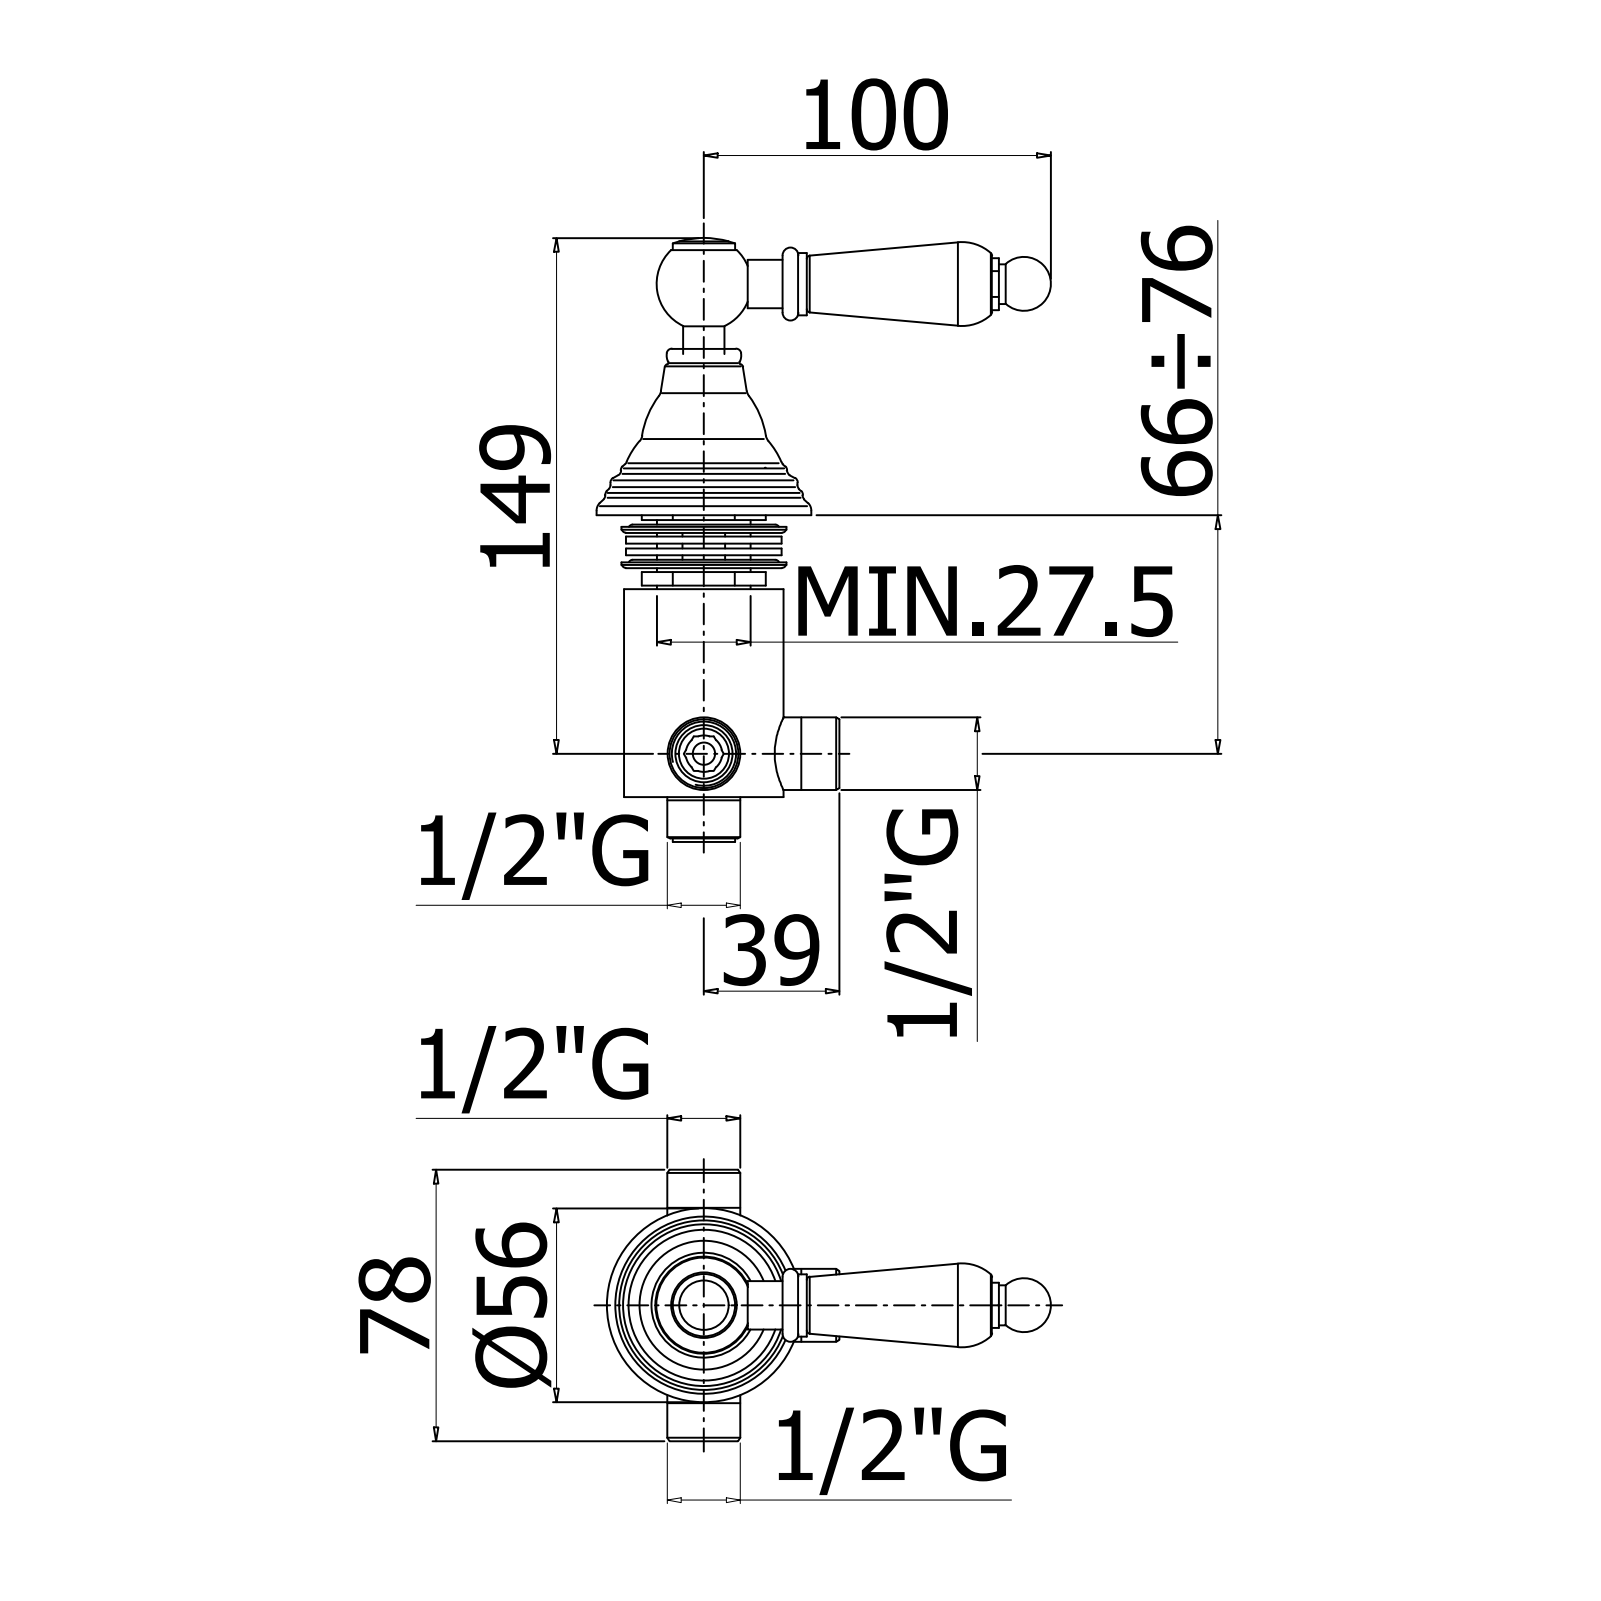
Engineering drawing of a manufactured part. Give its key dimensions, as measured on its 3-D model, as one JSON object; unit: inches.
{"part_name": "ZDEV108CR", "step_written_by": "CREO PARAMETRIC BY PTC INC, 2020044 (CONFIG_CONTROL_DESIGN)", "units": "inches", "bodies": {"solids": 5, "faces": 246, "planar": 83, "cylindrical": 48, "other": 115}, "overall_size": [5.106, 3.37, 2.48], "volume_in3": 3.51, "surface_area_in2": 48.96, "round_holes": [[0.244, 1], [0.354, 1], [0.453, 1], [0.551, 1], [0.587, 1], [0.787, 1], [0.866, 1], [1.012, 1], [1.016, 1], [1.079, 1], [1.083, 1], [2.37, 1]], "round_bosses_or_shafts": [[2.48, 1], [1.677, 1], [1.181, 1], [0.886, 1], [0.748, 1], [0.709, 1], [0.551, 1], [0.472, 1]], "face_to_face_distances": [0.024, 0.079, 0.035, 0.579, 0.224, 0.984, 0.114, 0.272, 0.102, 0.26]}
